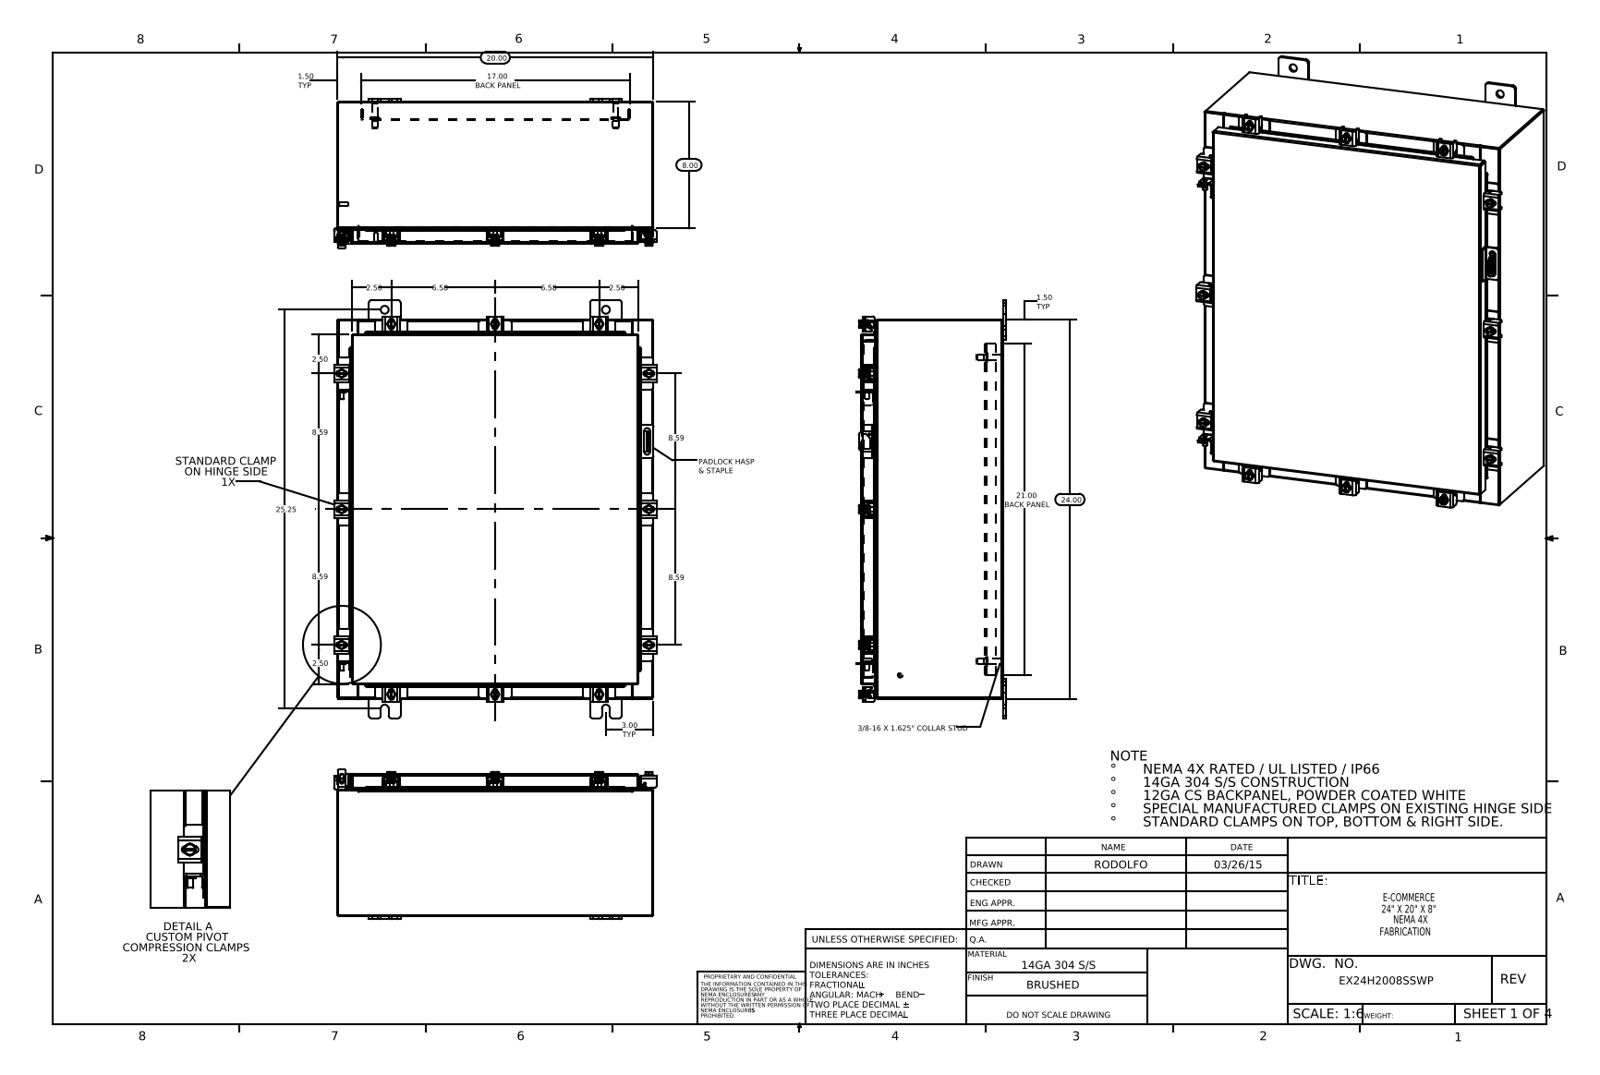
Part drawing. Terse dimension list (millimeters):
name: N-WMT04X30402202210-00 Clamp Top; HW-CLN-NH-20330; EX24H2008SSWP Bottom; EX24H2008SSWP Special Clamp (+8 more)
written by: SolidWorks 2014 (CONFIG_CONTROL_DESIGN)
unit: mm
bodies: 81 solids, 2018 faces (1075 planar, 783 cylindrical, 160 other)
size: 673.1 × 518.7 × 240.1
volume: 3 068 000 mm³; area: 3 023 000 mm²
holes: 12× ⌀5.4, 12× ⌀6.6, 8× ⌀12.7, 1× ⌀3.2, 1× ⌀6.4
bosses: 12× ⌀12.7, 12× ⌀6.4, 10× ⌀10.1, 4× ⌀15.9, 4× ⌀9.5, 4× ⌀8.4, 2× ⌀8, 2× ⌀6
rounds: 54× R1.5, 24× R0.3, 24× R3.6, 24× R4.8, 22× R2.2, 22× R3, 18× R2.3, 17× R1.3
face distances: 1.9, 226.1, 228, 224.2, 2.6, 506.1, 25.4, 27.3, 198.8, 200.7
hole spacings: 59.6, 112.8, 218.3, 308.4, 421.7, 465.8, 510.1, 522.3
